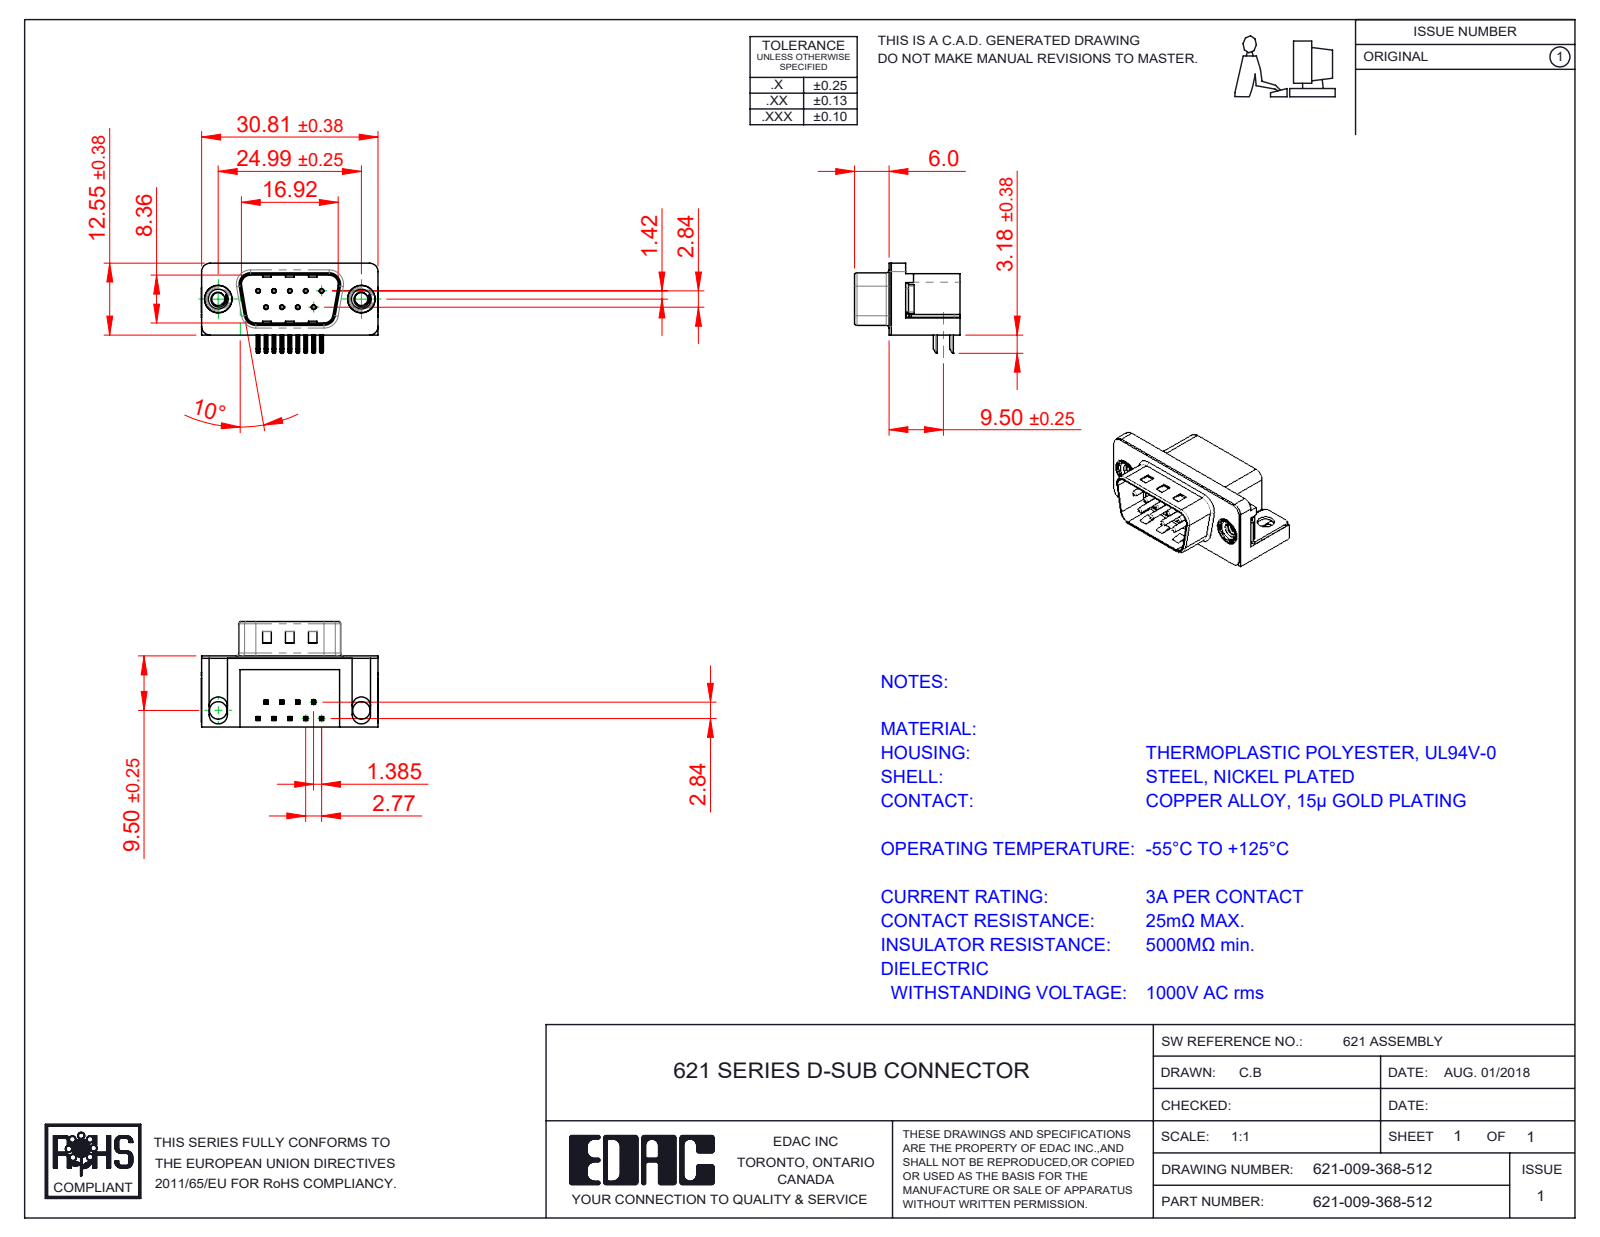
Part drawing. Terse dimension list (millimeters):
name: 621 Shell_9 Socket; 621 Contact Bottom; 621 4-40 Threaded Rivet; 621 Contact Top (+3 more)
written by: SolidWorks 2016 (CONFIG_CONTROL_DESIGN)
unit: mm
bodies: 15 solids, 989 faces (571 planar, 315 cylindrical, 103 other)
size: 30.89 × 18.4 × 15.73
volume: 3 245 mm³; area: 4 408 mm²
holes: 9× ⌀0.35, 9× ⌀0.8, 2× ⌀2.26, 2× ⌀3.05, 2× ⌀4, 2× ⌀4.8, 2× ⌀5
bosses: 9× ⌀0.75, 2× ⌀4.9, 2× ⌀4.75, 2× ⌀3.9
rounds: 44× R0.25, 18× R0.12, 16× R1, 9× R0.5, 8× R1.5, 8× R1.6, 4× R0.9, 4× R2
face distances: 0.4, 12, 12.4, 10.35, 0.5, 2.9, 9.5, 2.5, 2.1, 0.35
hole spacings: 3.16, 2.77, 5.54, 5.03, 5.04, 8.31, 7.48, 7.49
